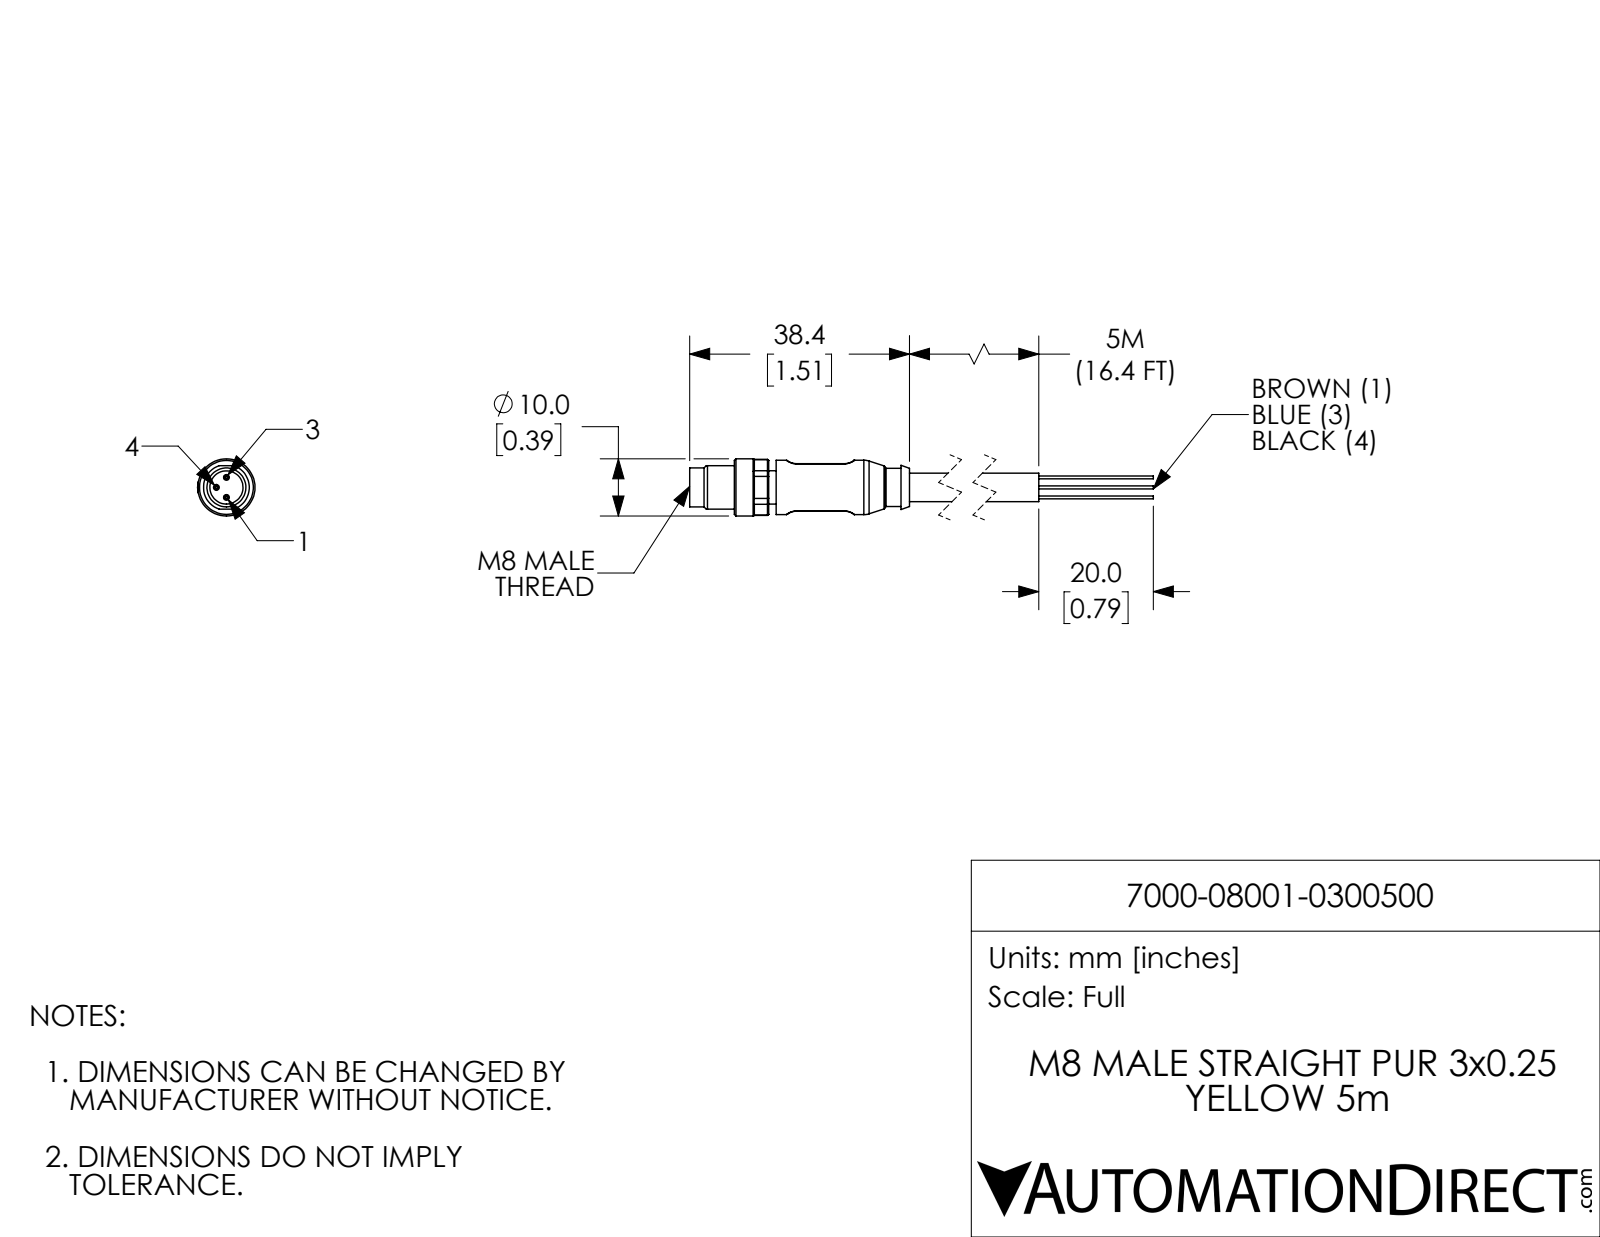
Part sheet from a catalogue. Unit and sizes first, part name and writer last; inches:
Units: inches
Overall size (bounding box): 3.087 × 0.396 × 0.394
Round holes (diameter × count): ⌀0.228 ×1
Round bosses / shafts (diameter × count): ⌀0.039 ×3, ⌀0.02 ×3, ⌀0.394 ×1, ⌀0.374 ×1, ⌀0.315 ×1, ⌀0.268 ×1, ⌀0.264 ×1, ⌀0.197 ×1
Partial cylindrical surfaces — rounded edges, fillets, slot ends (radius × count): R0.008 ×4, R0.098 ×4, R0.193 ×1, R0.199 ×1
Main face-to-face distances: 0.327, 0.051, 0.354, 0.014, 0.313, 0.346, 0.398, 2.102, 1.756, 1.705
Volume: 0.155 in³ · Surface area: 2.792 in²
Bodies: 4 solids, 119 faces (41 planar, 44 cylindrical, 34 other)
Part name (STEP PRODUCT): 7000-08001-0300500
STEP written by: SolidWorks 2021 (CONFIG_CONTROL_DESIGN)
